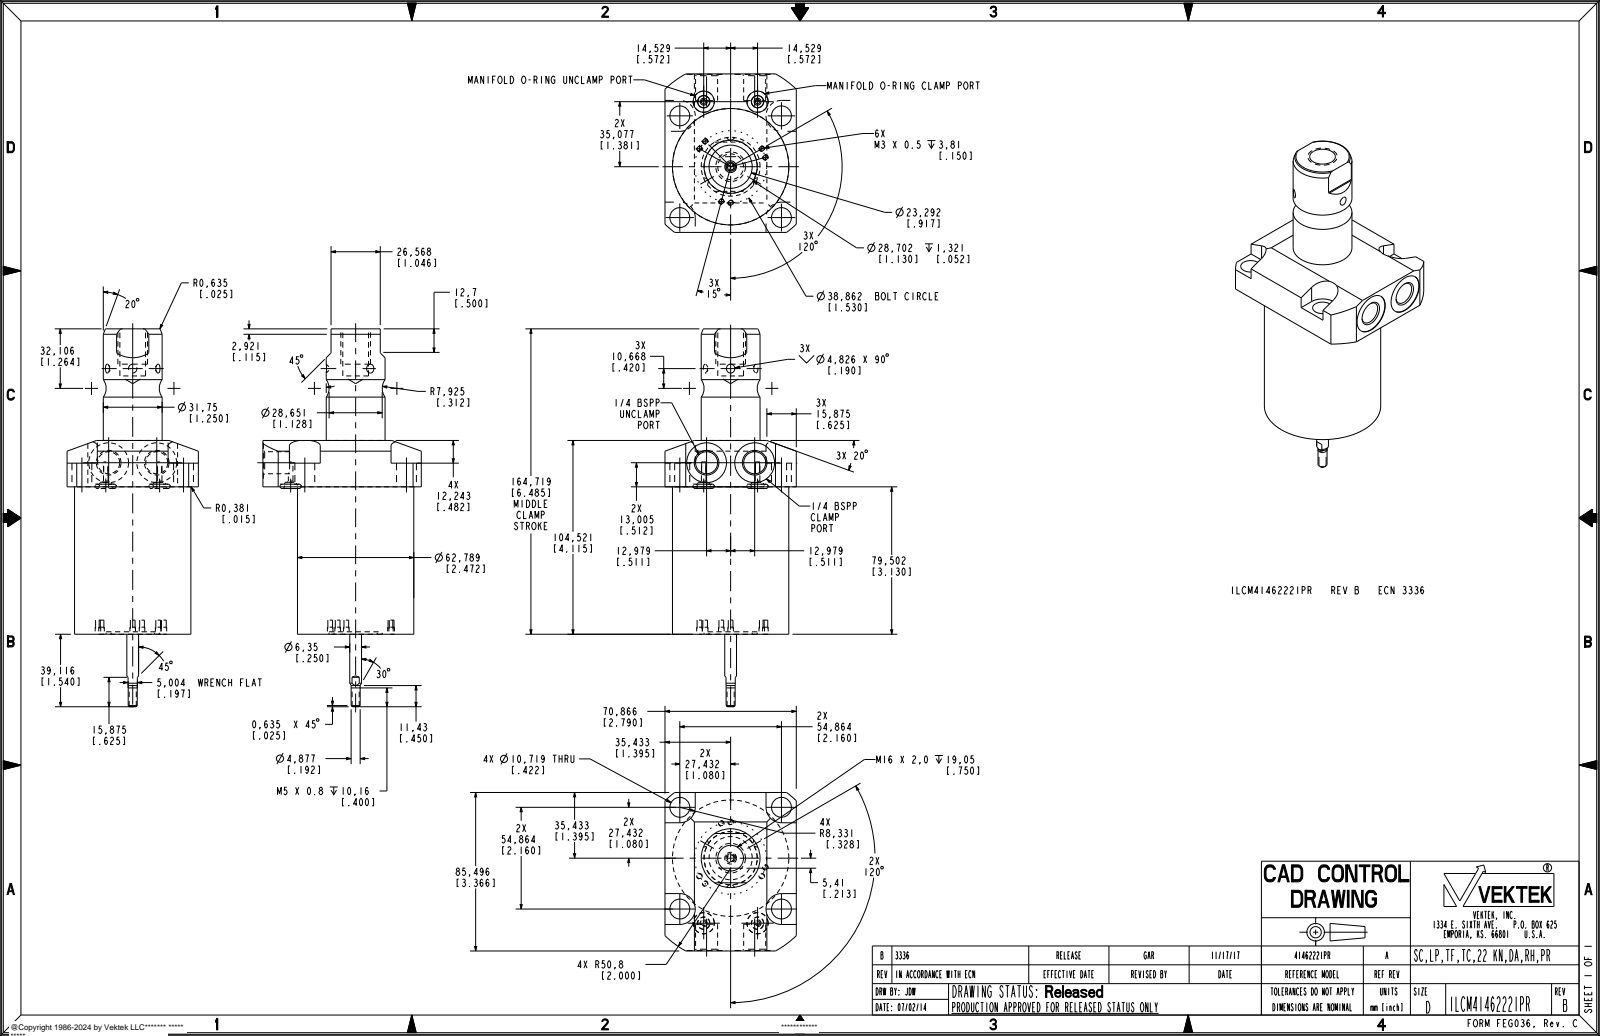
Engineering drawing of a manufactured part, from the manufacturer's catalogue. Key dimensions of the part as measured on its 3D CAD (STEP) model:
Part name (STEP PRODUCT): ILCM41462221PR
STEP written by: PRO/ENGINEER BY PARAMETRIC TECHNOLOGY CORPORATION, 2013320 (AUTOMOTIVE_DESIGN)
Units: millimetres
Bodies: 3 solids, 178 faces (60 planar, 82 cylindrical, 36 other)
Overall size (bounding box): 203.84 × 85.5 × 70.87
Volume: 411 065 mm³ · Surface area: 46 900 mm²
Round holes (diameter × count): ⌀2.54 ×6, ⌀10.72 ×4, ⌀2.49 ×2, ⌀6.5 ×2, ⌀11.4 ×2, ⌀11.89 ×2, ⌀21.49 ×2, ⌀13.87 ×1, ⌀28.7 ×1
Round bosses / shafts (diameter × count): ⌀3 ×6, ⌀62.79 ×1, ⌀31.75 ×1, ⌀23.29 ×1, ⌀16 ×1, ⌀6.35 ×1, ⌀4.88 ×1, ⌀3.86 ×1
Partial cylindrical surfaces — rounded edges, fillets, slot ends (radius × count): R8.33 ×4, R0.7 ×2, R50.8 ×1
Main face-to-face distances: 79.5, 104.52, 25.02, 70.86, 92.28, 12.78, 12.24, 164.72, 85.22, 72.44
Hole centre spacings: 33.66, 19.43, 38.79, 54.86, 5.07, 15, 19.44, 20.64
